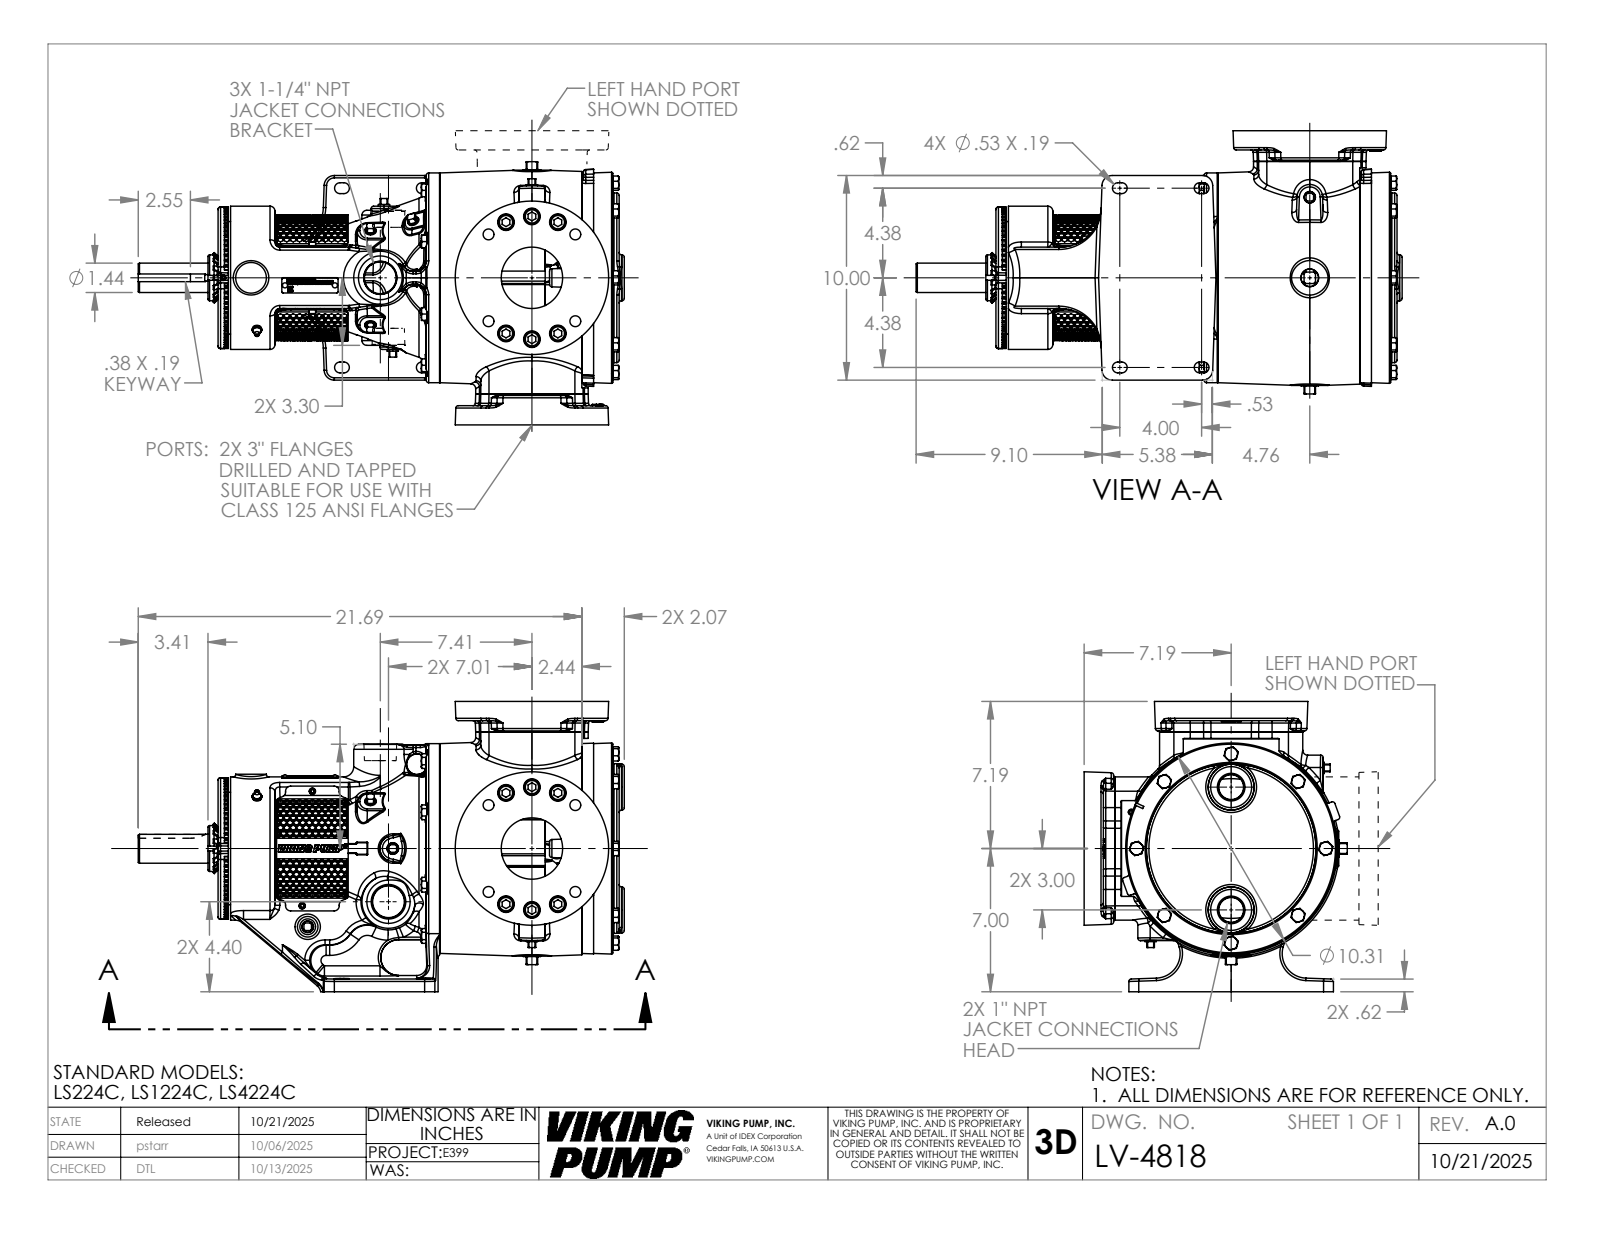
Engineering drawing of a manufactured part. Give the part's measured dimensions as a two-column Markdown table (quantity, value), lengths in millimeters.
| quantity | value |
| --- | --- |
| part name | LV-4818 |
| STEP written by | SolidWorks 2024 (AUTOMOTIVE_DESIGN) |
| units | millimeters |
| bodies | 1 solid, 5043 faces (1504 planar, 914 cylindrical, 2625 other) |
| overall size | 603.5 × 360.4 × 326.7 |
| volume | 21 270 000 mm³ |
| surface area | 932 900 mm² |
| round holes (diameter × count) | 20.6 × 12, 6.4 × 9, 13.5 × 8, 27.8 × 8, 5.1 × 6, 4 × 3, 6.8 × 2, 8 × 2, 76.2 × 2, 11.5 × 1, 38.3 × 1, 40.1 × 1 |
| round bosses / shafts (diameter × count) | 19.1 × 12, 15.9 × 9, 15.9 × 7, 7.9 × 3, 4.8 × 3, 260.4 × 1, 177.8 × 1, 139.6 × 1 |
| partial cylindrical surfaces (radius × count) | 1.6 × 109, 1.8 × 74, 3 × 70, 0.3 × 56, 12.7 × 26, 0.8 × 18, 6.1 × 16, 25.4 × 16 |
| main face-to-face distances | 360.3, 7.9, 57.2, 330.4, 338.3, 89.9, 420.3, 428.2, 12.7, 69.9 |
| hole center spacings | 76.2, 107.8, 152.4, 34.9, 26.5, 33, 55.4, 58.3 |
